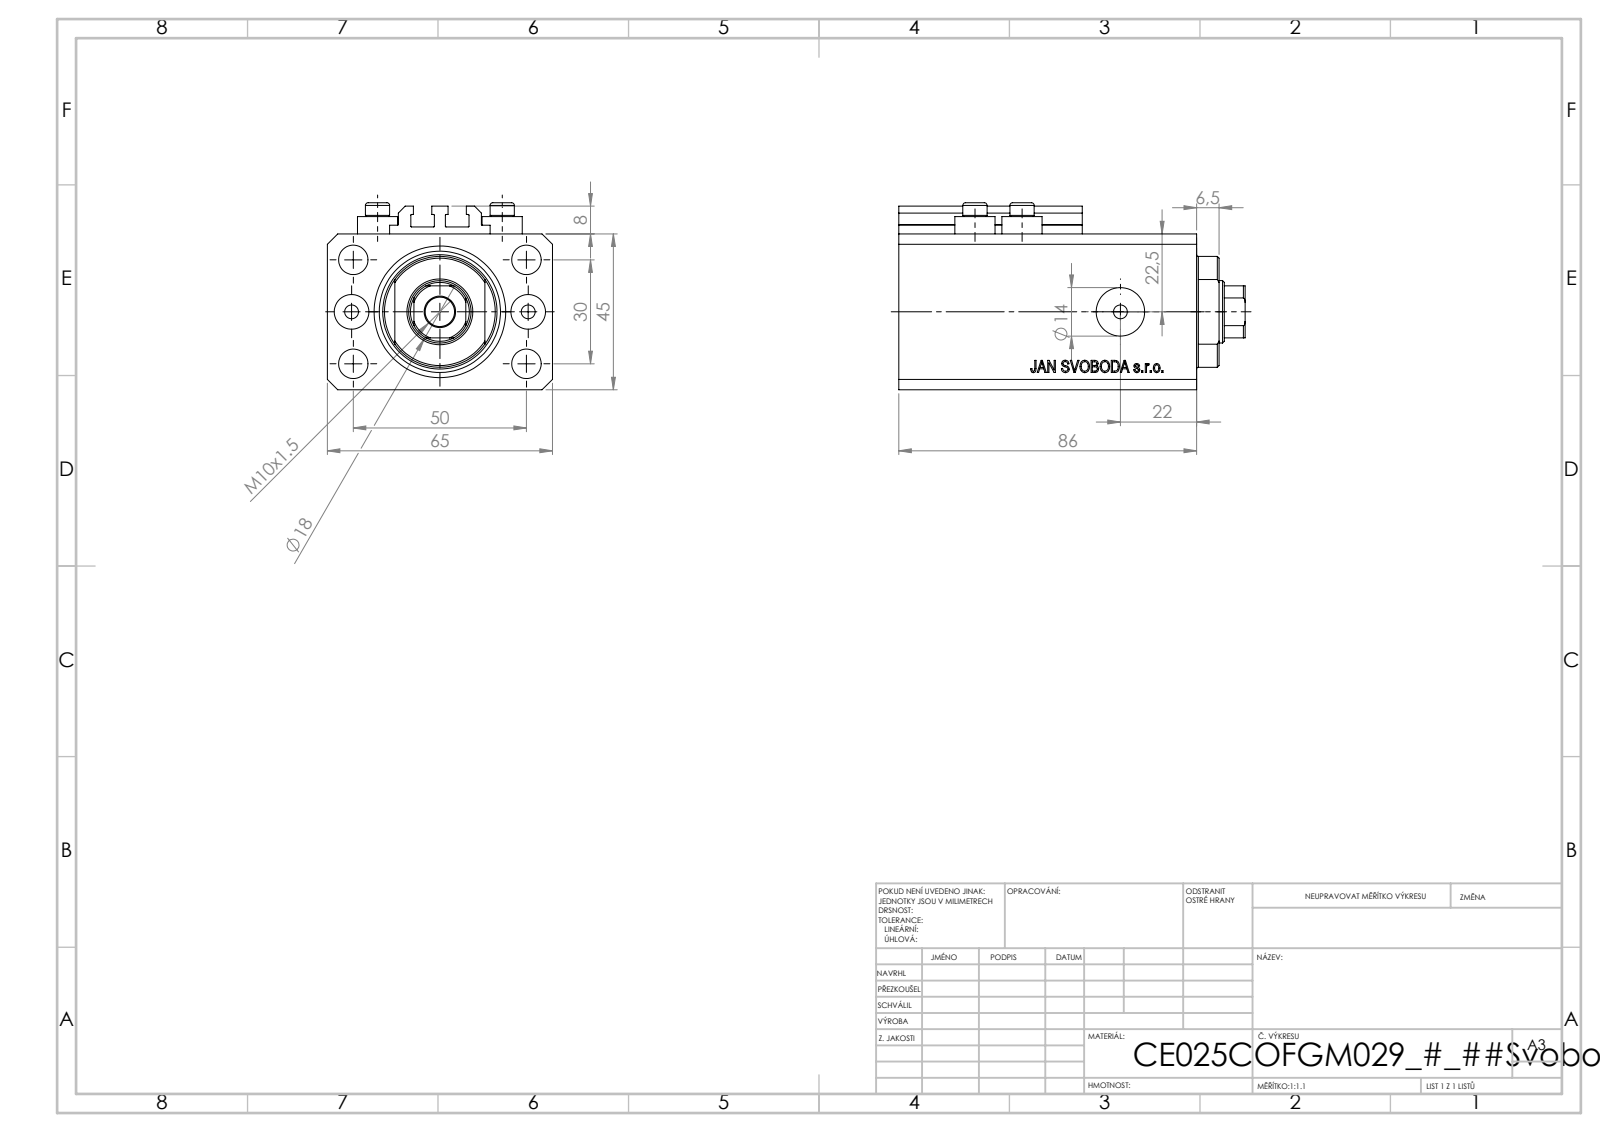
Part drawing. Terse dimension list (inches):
name: V250CE_C_Body; V250CE_VC_C; V250CE_C_VCP; ALLEN BOLT V250CE
written by: SolidWorks 2019 (CONFIG_CONTROL_DESIGN)
unit: in
bodies: 8 solids, 1034 faces (504 planar, 86 cylindrical, 444 other)
size: 3.937 × 2.559 × 2.126
volume: 14.34 in³; area: 96.51 in²
holes: 8× ⌀0.157, 5× ⌀0.335, 2× ⌀0.394, 2× ⌀0.551, 1× ⌀0.709, 1× ⌀0.984, 1× ⌀1.496
bosses: 4× ⌀0.457, 4× ⌀0.276
rounds: 10× R0.008, 1× R0.335, 1× R0.63
face distances: 1.772, 2.559, 0.551, 2.835, 3.386, 1.85, 0.272, 2.563, 3.114, 0.118
hole spacings: 0.591, 1.148, 2.074, 0.535, 1.004, 1.181, 1.417, 1.515
